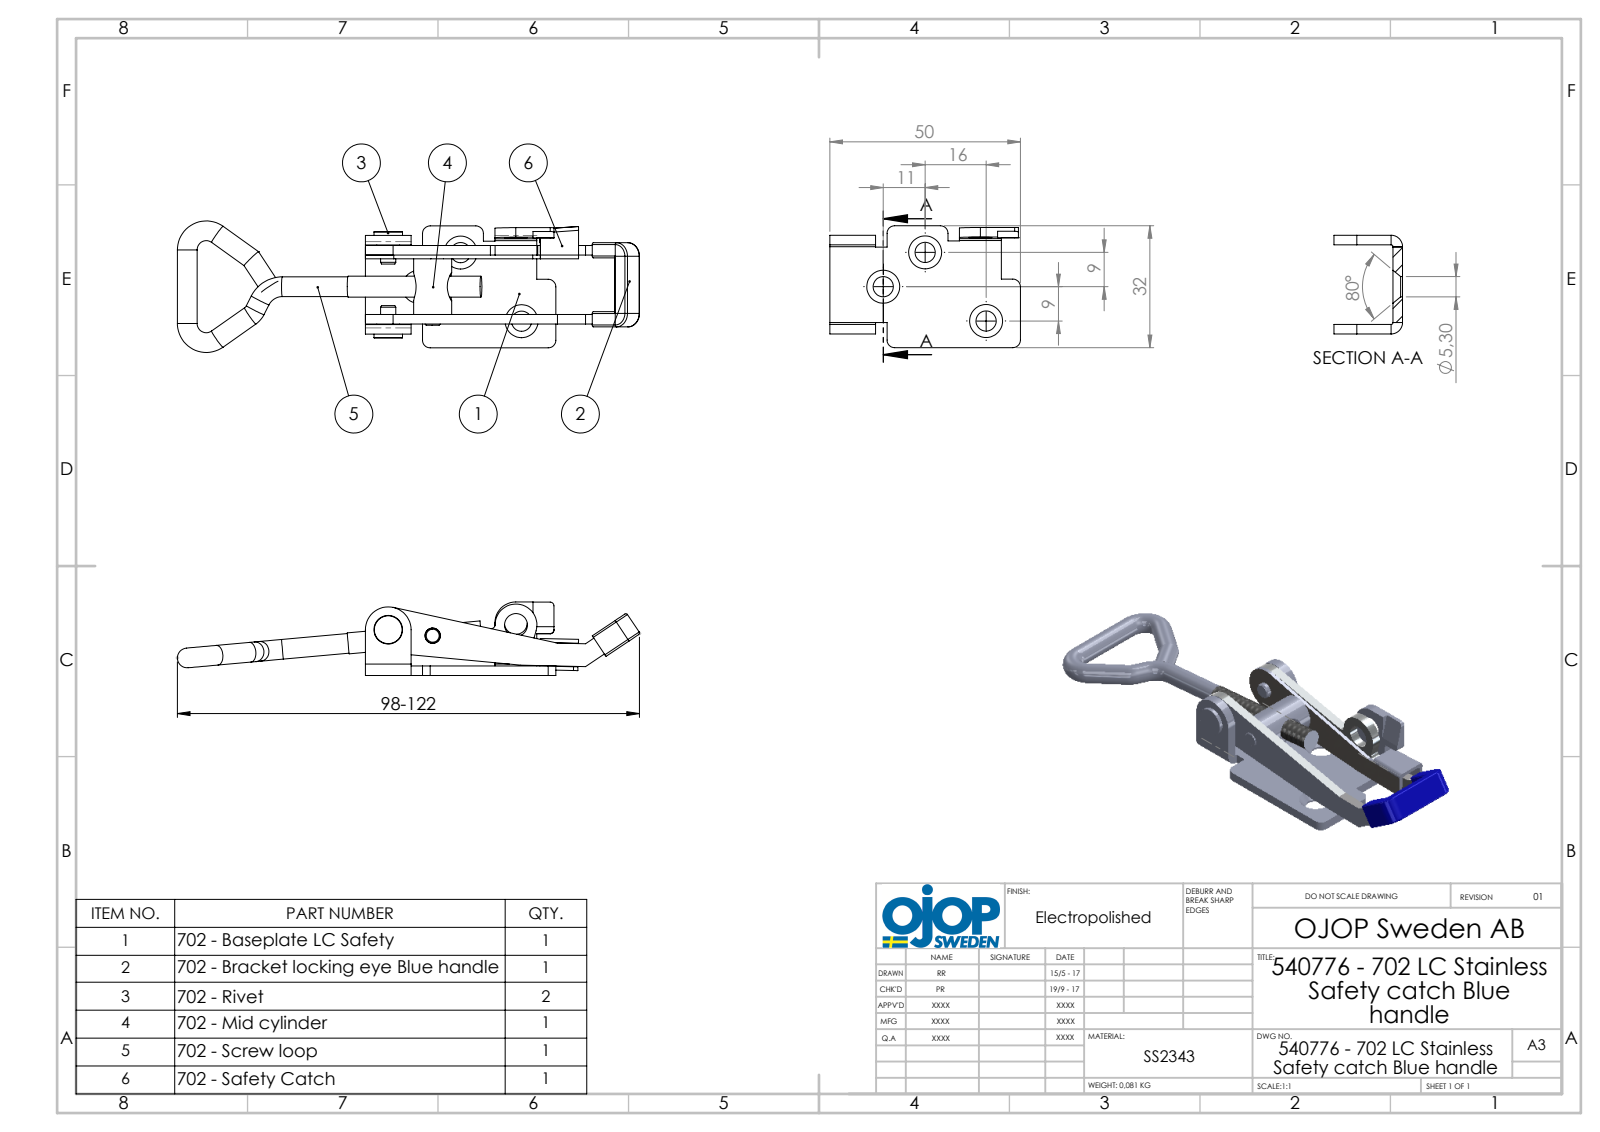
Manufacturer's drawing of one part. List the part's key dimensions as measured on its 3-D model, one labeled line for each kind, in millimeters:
Part name (STEP PRODUCT): 702 - Ansatsnit; 702 - Rulle; 702 - Skruvögla; 702 - Platta LC Spärr (+3 more)
STEP written by: SolidWorks 2015 (AUTOMOTIVE_DESIGN)
Units: millimetres
Bodies: 7 solids, 255 faces (104 planar, 109 cylindrical, 42 other)
Overall size (bounding box): 121.3 × 34.52 × 19.3
Volume: 12 829 mm³ · Surface area: 13 100 mm²
Round holes (diameter × count): ⌀5.3 ×3, ⌀6 ×3, ⌀4 ×2, ⌀4.1 ×2, ⌀5 ×1
Round bosses / shafts (diameter × count): ⌀5.18 ×6, ⌀10 ×1, ⌀7.5 ×1, ⌀5.5 ×1
Partial cylindrical surfaces — rounded edges, fillets, slot ends (radius × count): R0.5 ×15, R1 ×11, R2 ×5, R3 ×3, R0.45 ×2, R3.55 ×2, R5.5 ×2, R6 ×1
Main face-to-face distances: 2.5, 18.1, 1, 20.75, 3.5, 15.6, 2.65, 20.6, 14.6, 17.1
Hole centre spacings: 11.77, 14.21, 22.05, 24.08, 28.46, 33.56
